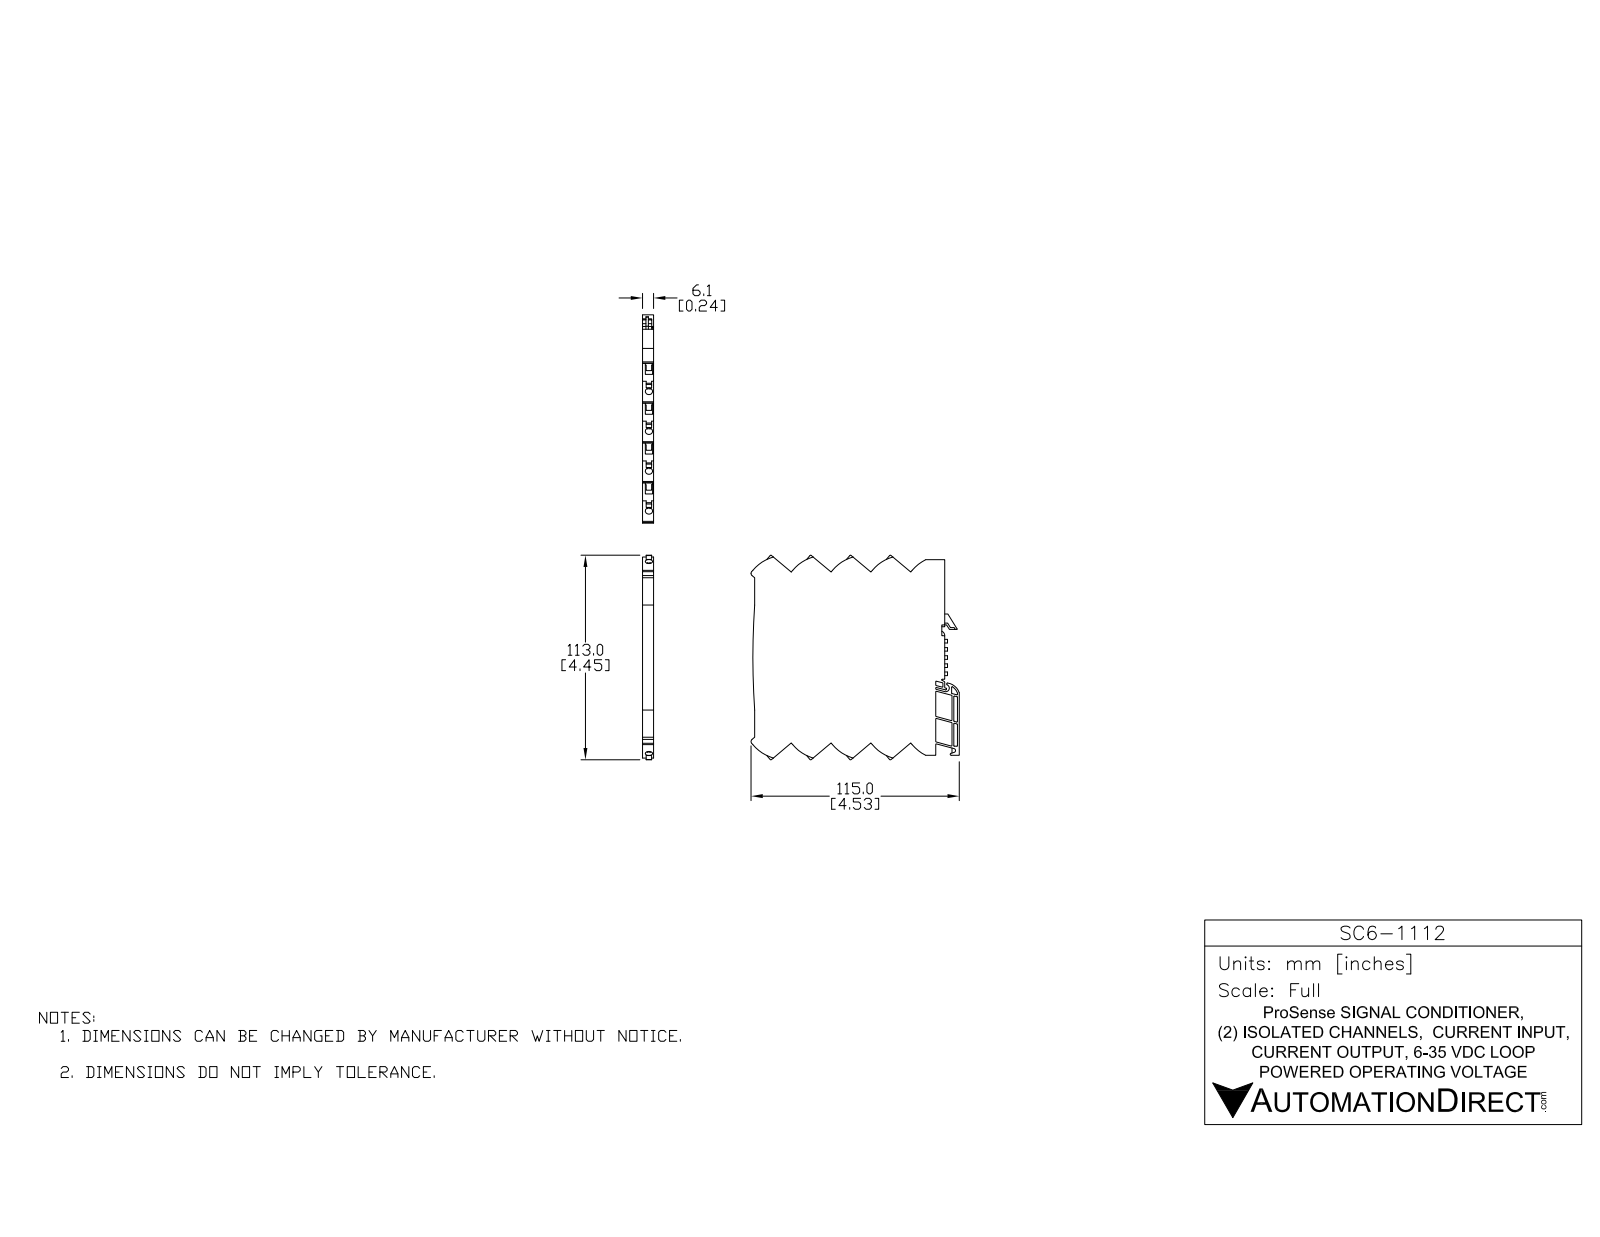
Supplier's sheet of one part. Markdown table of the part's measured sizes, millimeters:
| quantity | value |
| --- | --- |
| part name | SC6-1112 |
| STEP written by | SolidWorks 2017 (AUTOMOTIVE_DESIGN) |
| units | millimeters |
| bodies | 1 solid, 435 faces (328 planar, 107 cylindrical, 0 other) |
| overall size | 115 × 112.99 × 6.1 |
| volume | 65 156 mm³ |
| surface area | 28 033 mm² |
| round holes (diameter × count) | 4 × 8 |
| partial cylindrical surfaces (radius × count) | 0.3 × 33, 0.5 × 10, 1.5 × 10, 23.31 × 10, 0.2 × 2, 0.57 × 1, 1.08 × 1, 2 × 1 |
| main face-to-face distances | 6.1, 1, 3, 4, 2.05, 14.14, 4.05, 1.05, 3.5, 5.05 |
| hole center spacings | 14.14, 28.28, 14.15, 42.42 |
